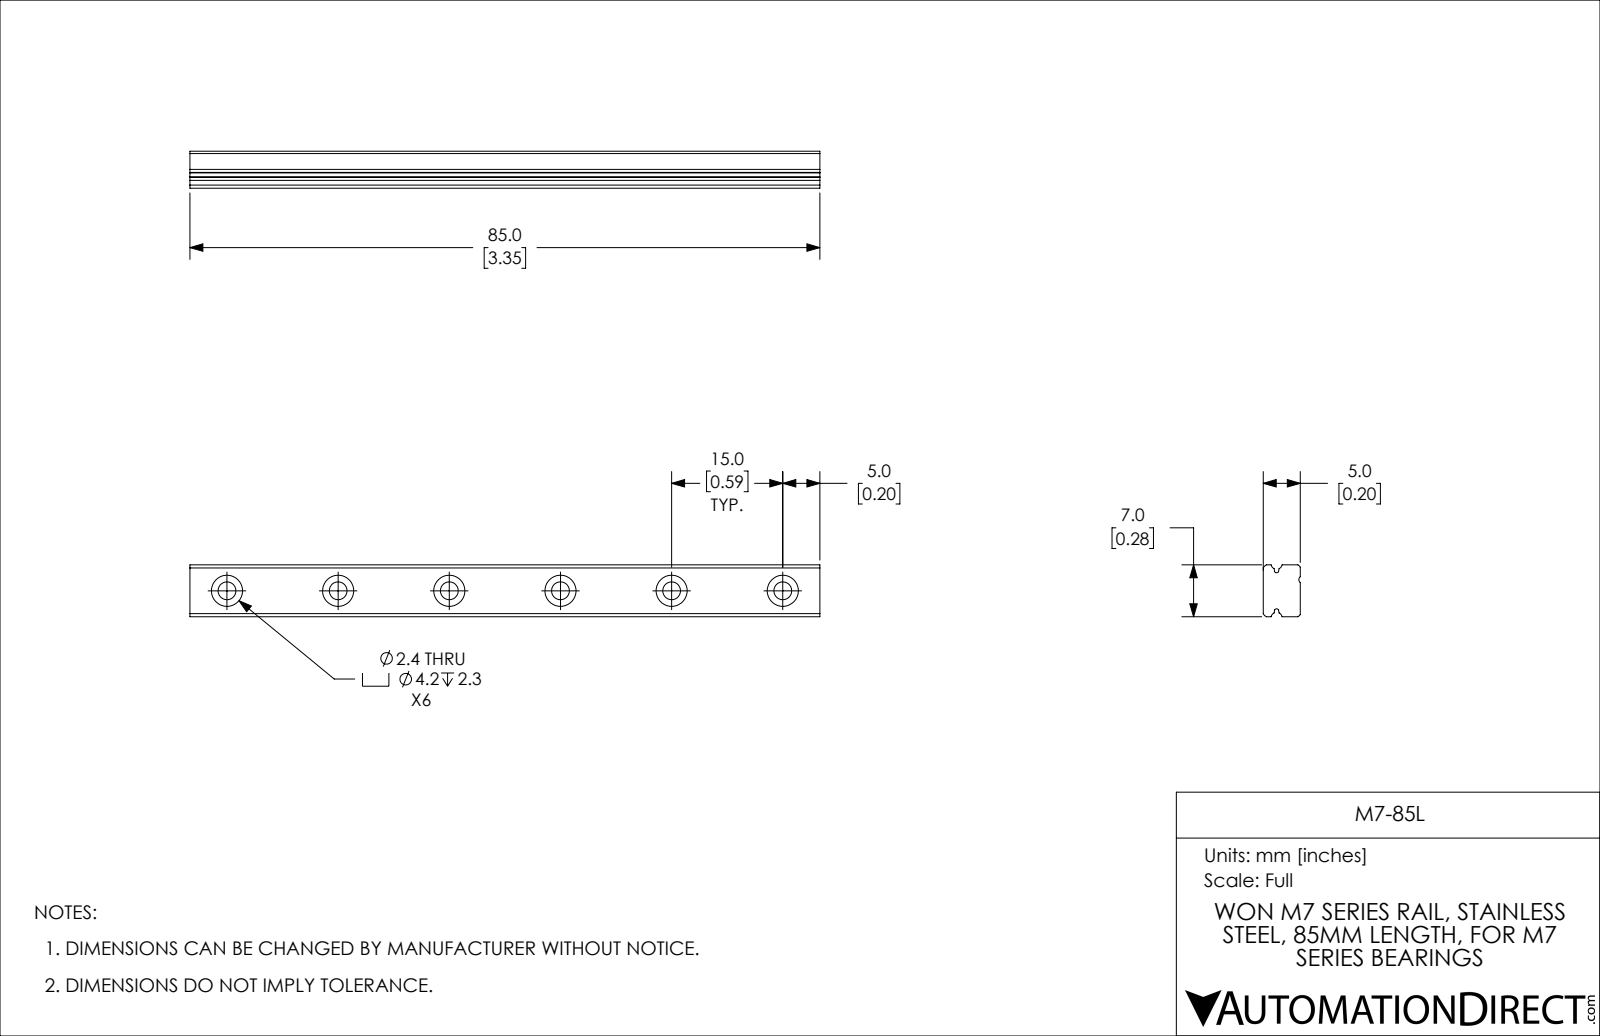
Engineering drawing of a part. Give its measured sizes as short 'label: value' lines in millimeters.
name: M7-85L
written by: SolidWorks 2019 (CONFIG_CONTROL_DESIGN)
unit: mm
bodies: 1 solid, 55 faces (19 planar, 36 cylindrical, 0 other)
size: 85 × 7 × 5
volume: 2 524 mm³; area: 2 521 mm²
holes: 6× ⌀2.4, 6× ⌀4.2
rounds: 2× R0.32, 2× R0.75, 2× R0.95, 2× R1, 1× R0.5
face distances: 5, 7, 0.36, 2.7, 2.3, 85
hole spacings: 15, 30, 45, 60, 75
